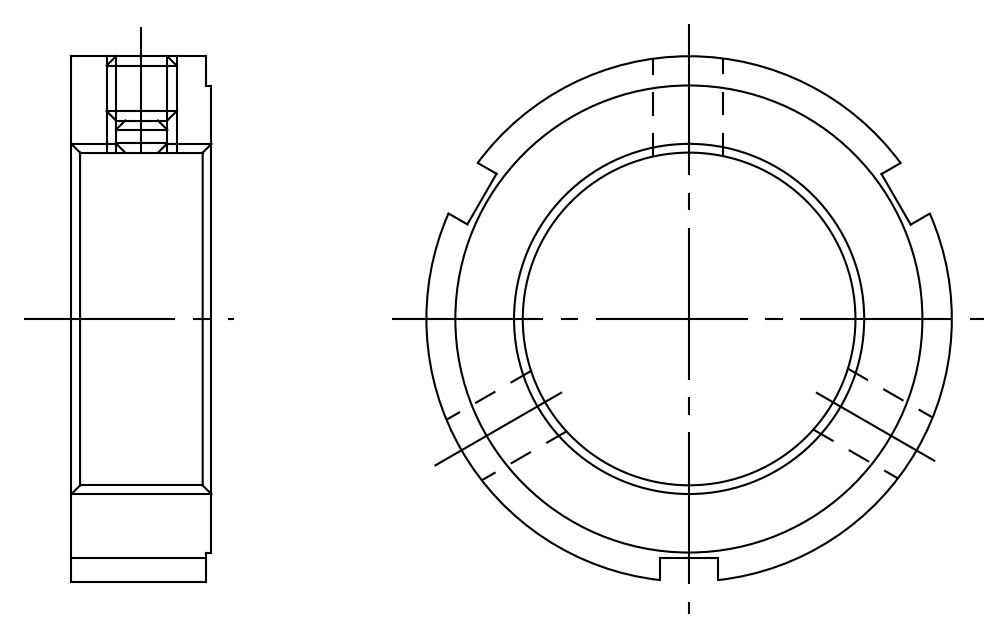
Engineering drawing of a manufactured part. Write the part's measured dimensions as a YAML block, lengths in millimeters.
part_name: "FKD ZMT 30"
step_written_by: "Autodesk Inventor 2011 (AUTOMOTIVE_DESIGN)"
units: millimeters
bodies: {solids: 1, faces: 22, planar: 12, cylindrical: 8, other: 2}
overall_size: [45, 44.86, 12]
volume: 9647
surface_area: 4837
round_holes:
  - {diameter: 4.92, count: 3}
  - {diameter: 30, count: 1}
round_bosses_or_shafts:
  - {diameter: 45, count: 1}
  - {diameter: 40, count: 1}
face_to_face_distances: [12, 0.5, 11.5, 5]
